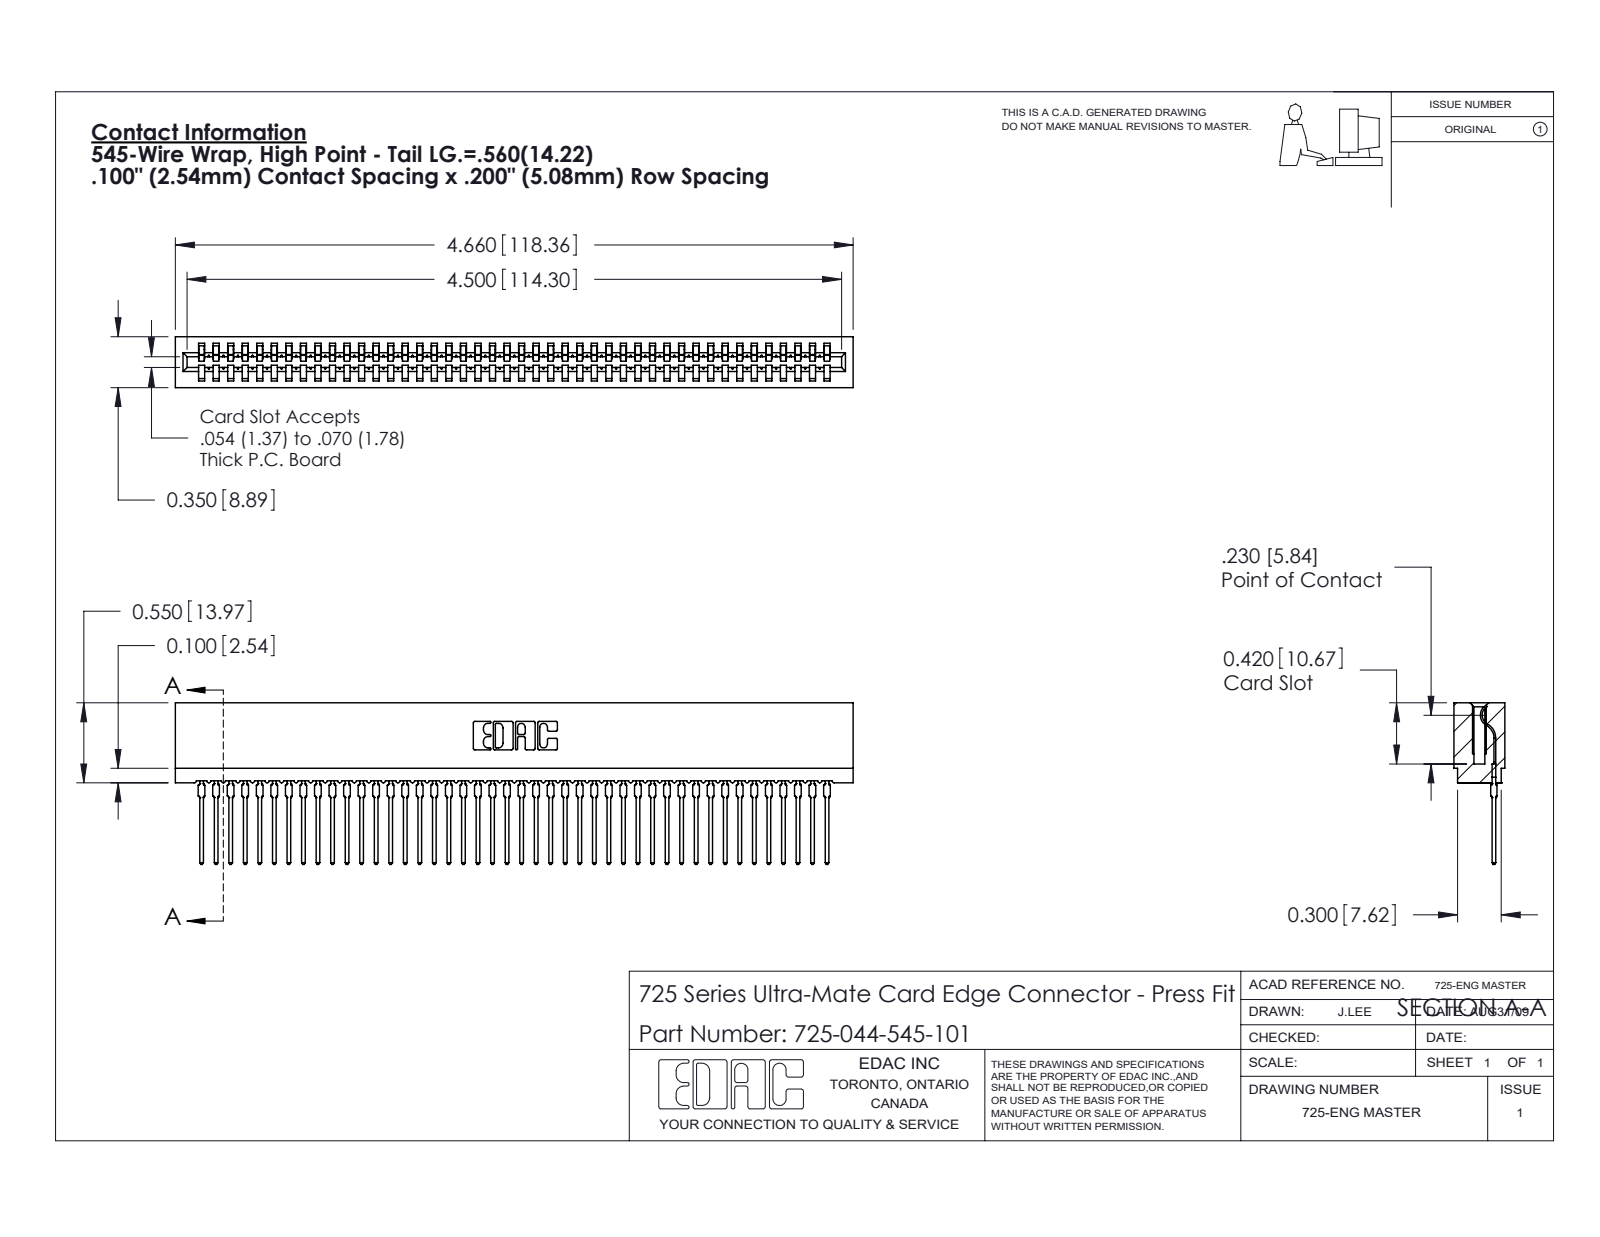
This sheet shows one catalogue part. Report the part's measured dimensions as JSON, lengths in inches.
{"part_name": "725 Part_Insulator Option - 01; 745-292-001_545; 725-044-545-101", "step_written_by": "SolidWorks 2020 (CONFIG_CONTROL_DESIGN)", "units": "inches", "bodies": {"solids": 45, "faces": 5023, "planar": 3003, "cylindrical": 876, "other": 1144}, "overall_size": [4.66, 1.111, 0.35], "volume_in3": 0.555, "surface_area_in2": 28.2, "partial_cylinders_radius": [[0.015, 88], [0.021, 88], [0.01, 22], [0.007, 6], [0.031, 6], [0.005, 4], [0.011, 4], [0.026, 3]], "face_to_face_distances": [0.35, 0.063, 0.287, 0.212, 0.138, 0.2, 0.045, 0.305, 0.093, 0.167]}
